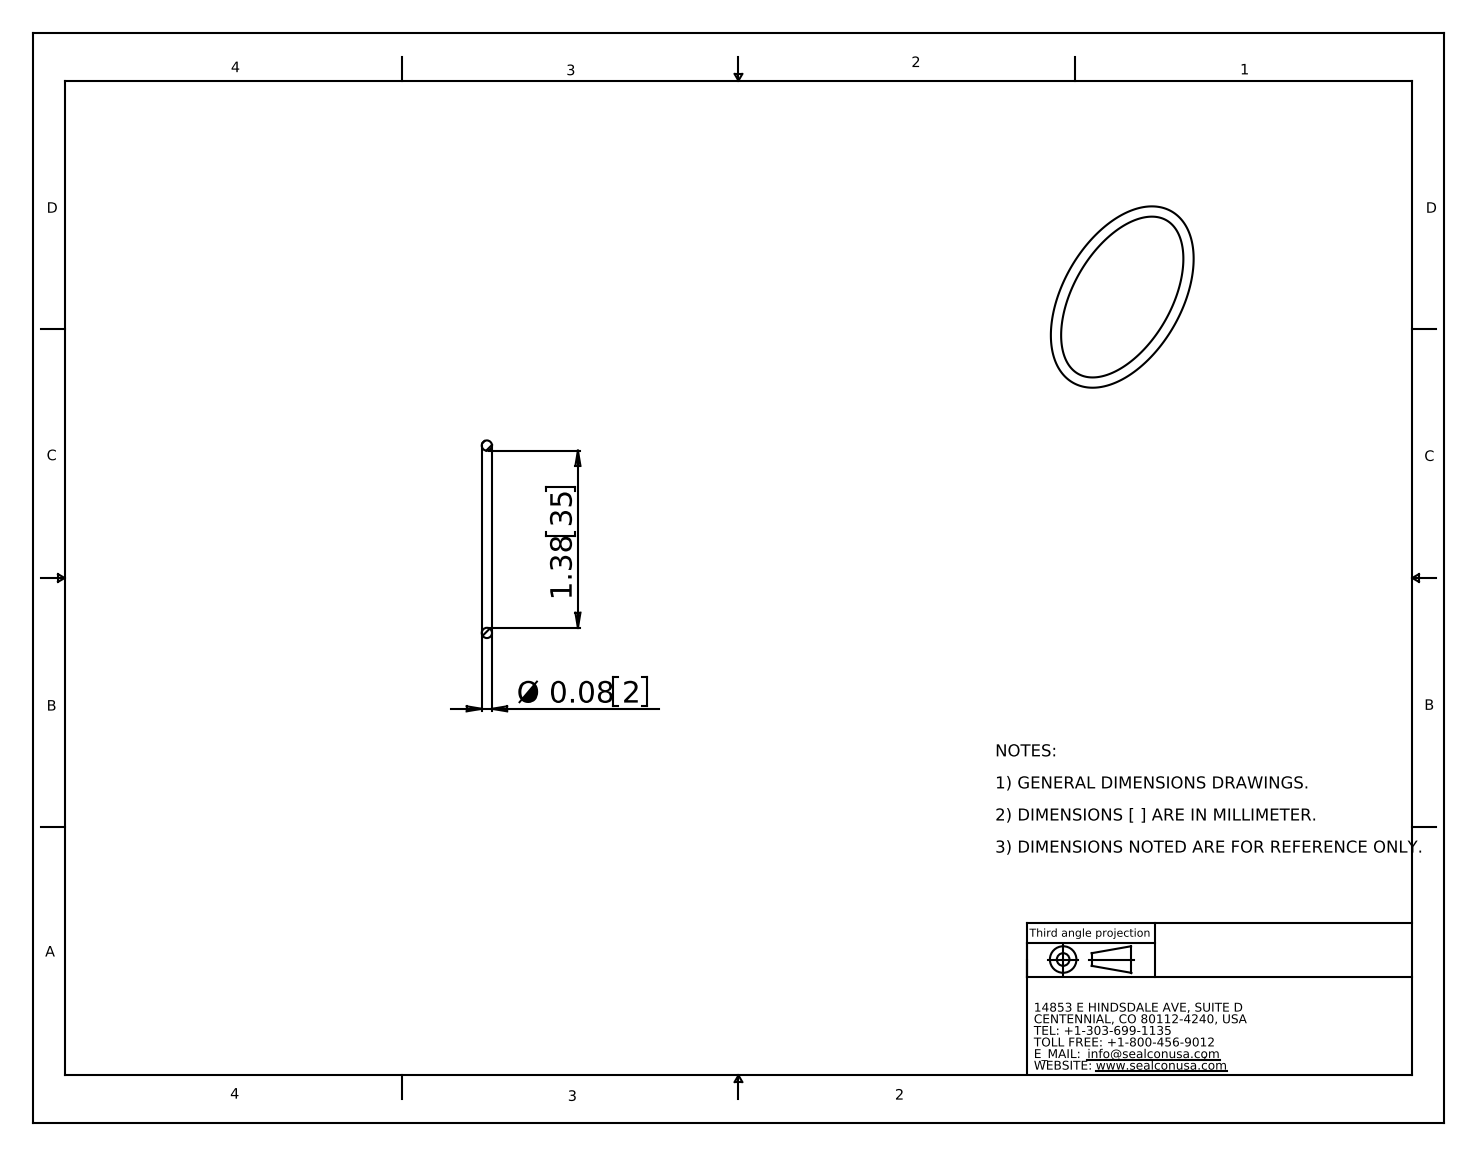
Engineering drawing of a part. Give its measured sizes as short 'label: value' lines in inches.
name: OM-40-SI
written by: SolidWorks 2008 (CONFIG_CONTROL_DESIGN)
unit: in
bodies: 1 solid, 4 faces (0 planar, 0 cylindrical, 4 other)
size: 1.54 × 1.54 × 0.08
volume: 0.023 in³; area: 1.153 in²
